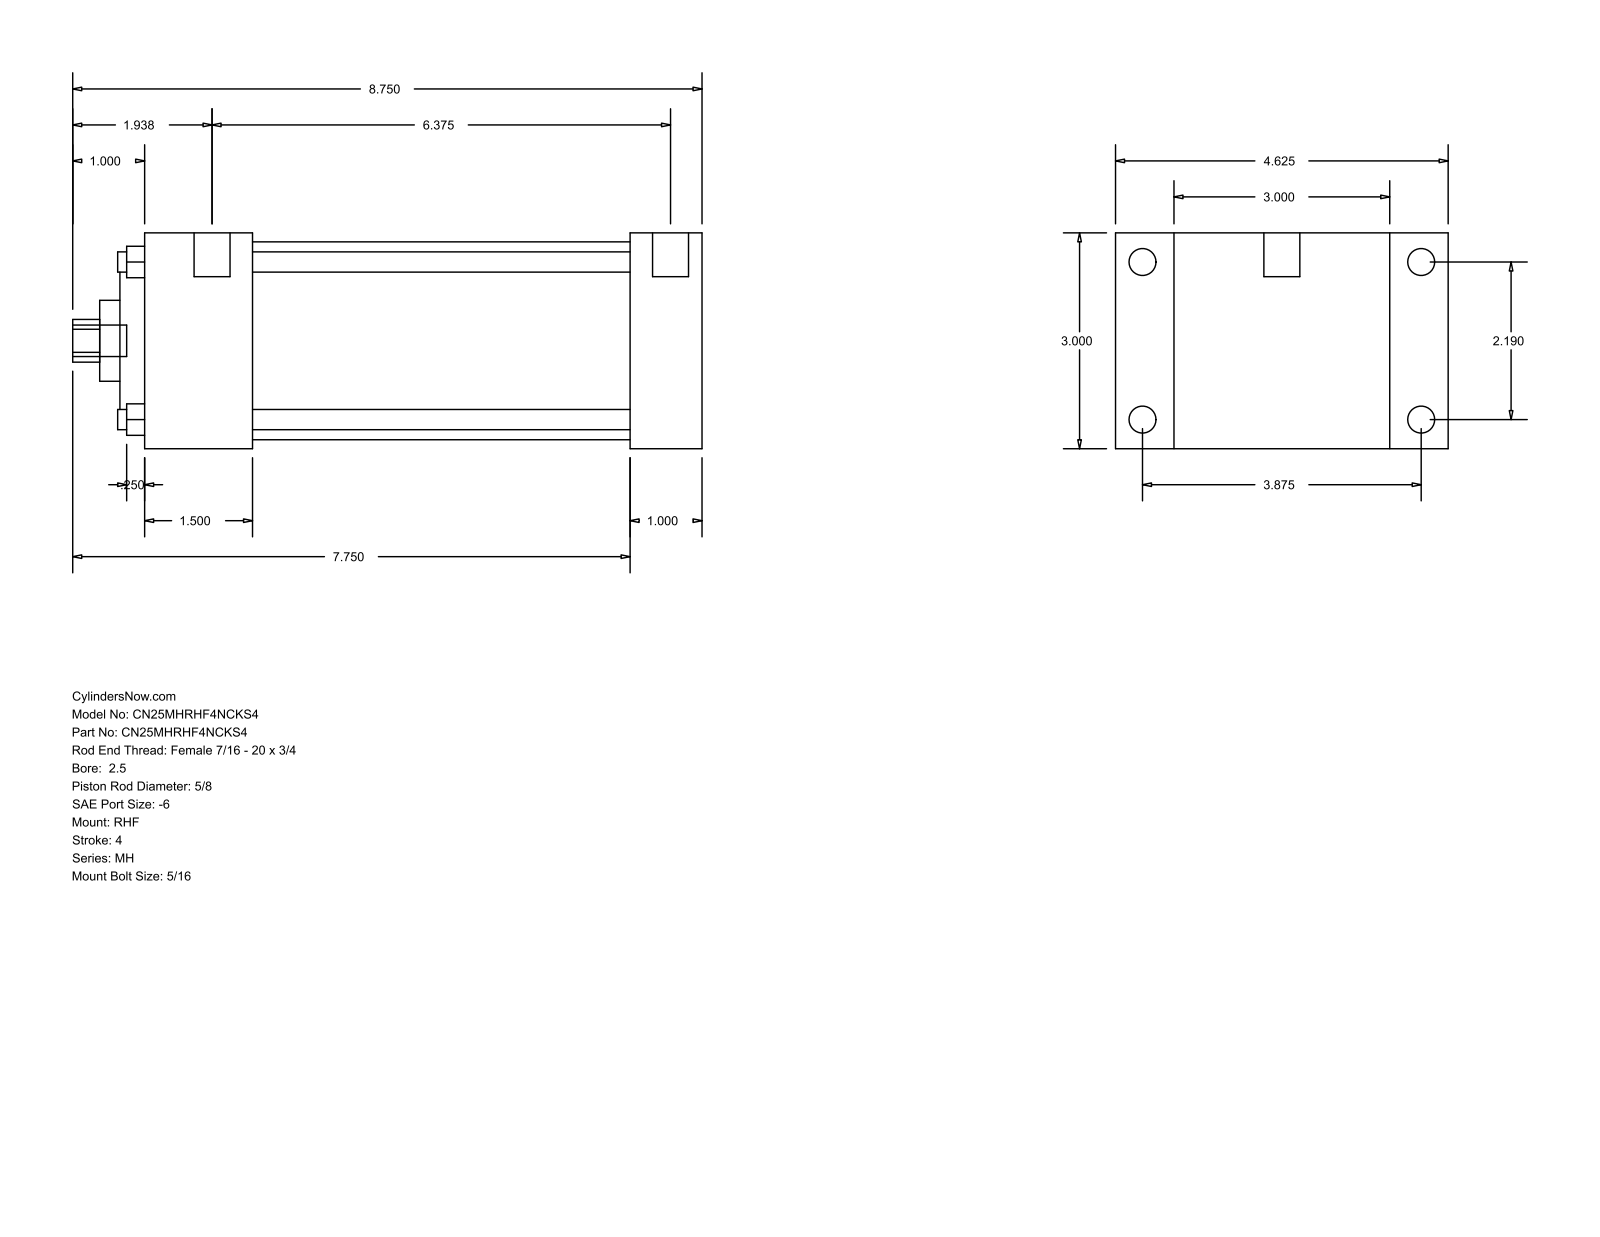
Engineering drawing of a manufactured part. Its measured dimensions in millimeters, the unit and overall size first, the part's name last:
Units: millimetres
Overall size (bounding box): 222.25 × 117.47 × 76.2
Round holes (diameter × count): ⌀7.14 ×4, ⌀15.88 ×1, ⌀28.57 ×1, ⌀55.55 ×1, ⌀69.85 ×1
Round bosses / shafts (diameter × count): ⌀9.53 ×4, ⌀5.56 ×4, ⌀12.7 ×2, ⌀11.11 ×1
Partial cylindrical surfaces — rounded edges, fillets, slot ends (radius × count): R7.54 ×1
Main face-to-face distances: 76.2, 25.4, 20.64, 96.84, 196.85, 171.45, 117.48, 38.1, 133.35, 158.75
Hole centre spacings: 39.33, 55.62, 78.66
Bodies: 0 solids, 90 faces (61 planar, 29 cylindrical, 0 other)
Part name (STEP PRODUCT): MH_RHF__0250_0.625
STEP written by: GSSL Pune (CONFIG_CONTROL_DESIGN)
